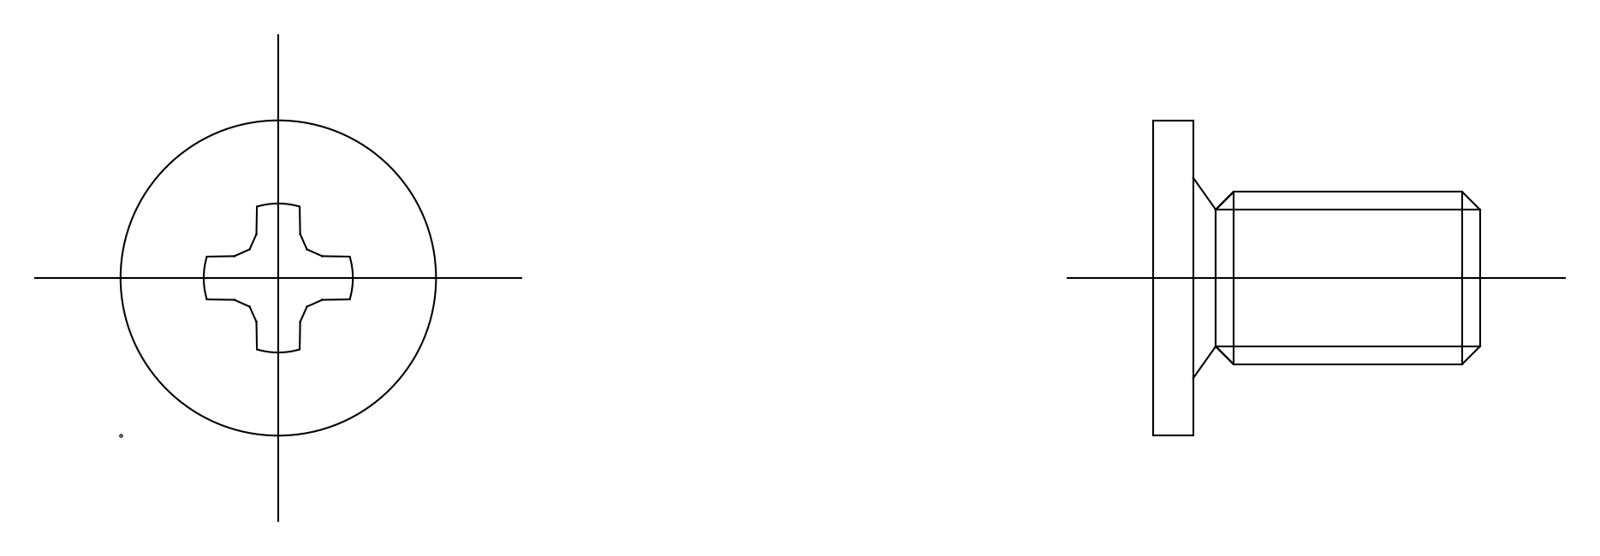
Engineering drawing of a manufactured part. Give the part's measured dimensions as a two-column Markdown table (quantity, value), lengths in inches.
| quantity | value |
| --- | --- |
| STEP written by | spGate 20.6.3 (****-****-****-****) (AUTOMOTIVE_DESIGN) |
| units | inches |
| bodies | 1 solid, 29 faces (19 planar, 4 cylindrical, 6 other) |
| overall size | 0.224 × 0.217 × 0.217 |
| volume | 0.003 in³ |
| surface area | 0.175 in² |
| round bosses / shafts (diameter × count) | 0.217 × 1, 0.118 × 1 |
| main face-to-face distances | 0.028, 0.224, 0.197, 0.052, 0.031 |
